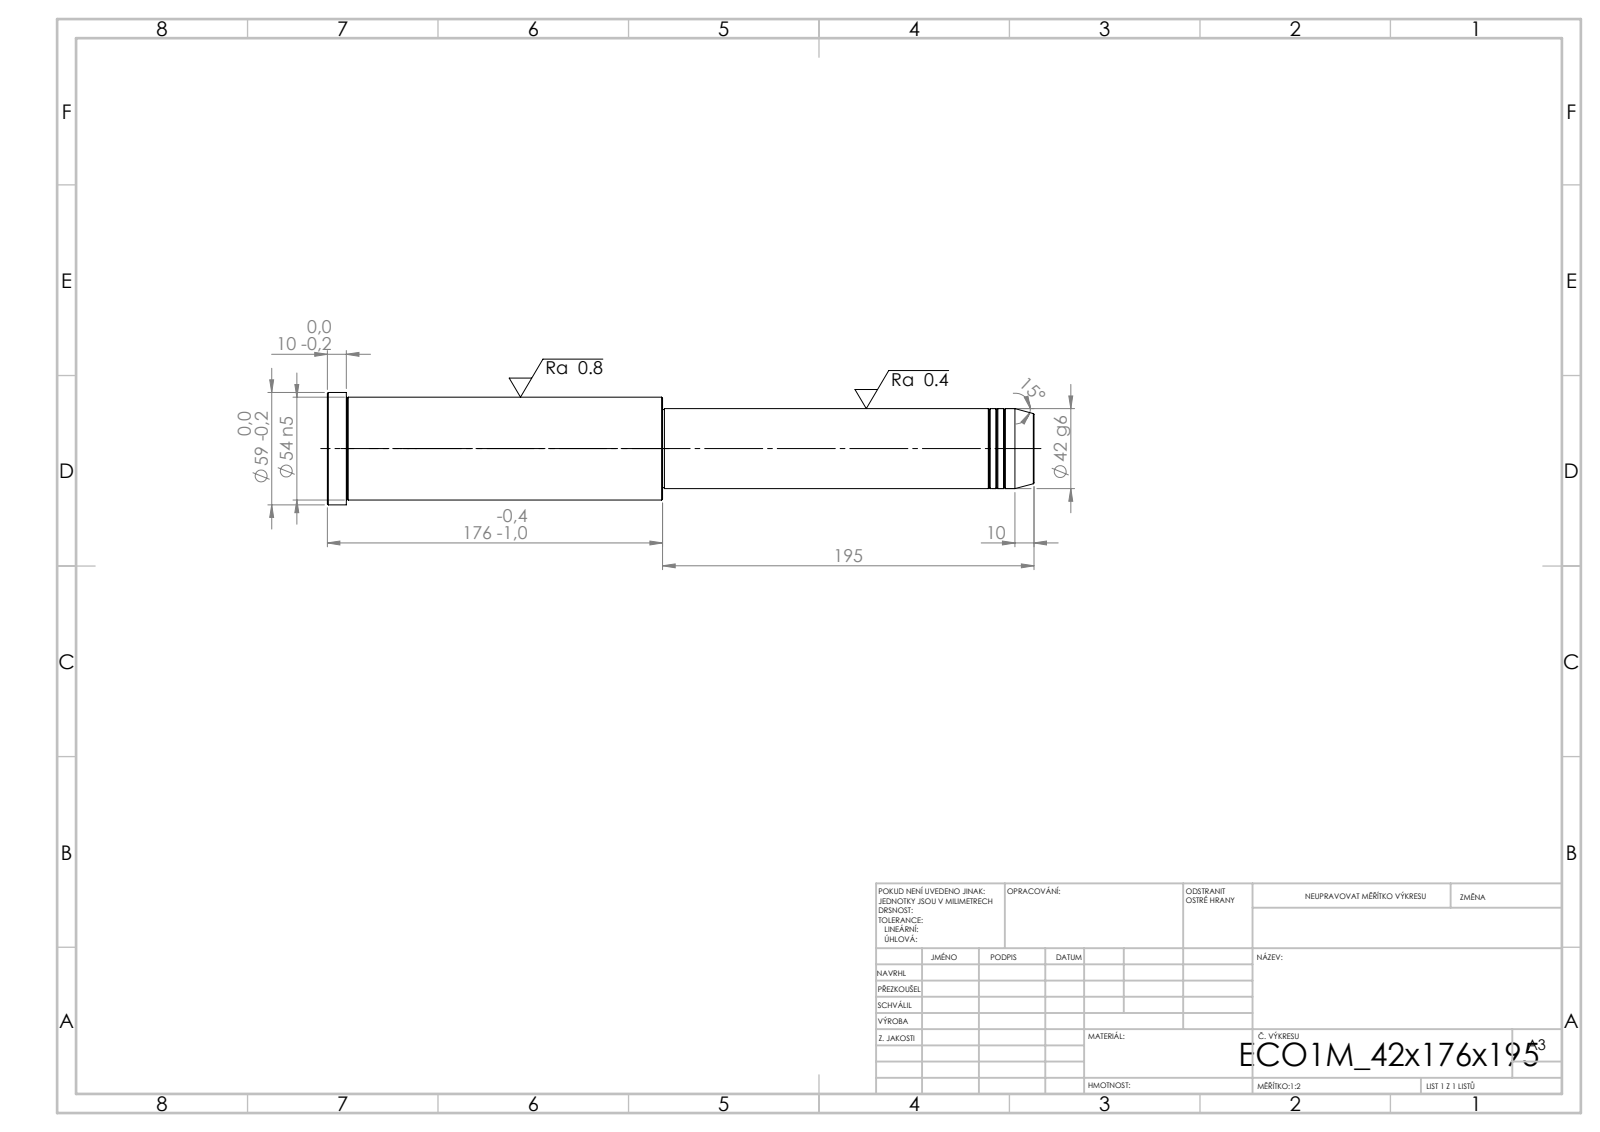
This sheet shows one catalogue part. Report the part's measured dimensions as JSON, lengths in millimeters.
{"step_written_by": "SolidWorks 2019 (CONFIG_CONTROL_DESIGN)", "units": "millimeters", "bodies": {"solids": 1, "faces": 43, "planar": 5, "cylindrical": 14, "other": 24}, "overall_size": [371, 59, 59], "volume_mm3": 675653, "surface_area_mm2": 61161, "round_bosses_or_shafts": [[59, 1], [54, 1], [42, 1], [41, 1]], "face_to_face_distances": [371, 195, 176, 361, 166, 10, 194, 1, 167, 177]}
